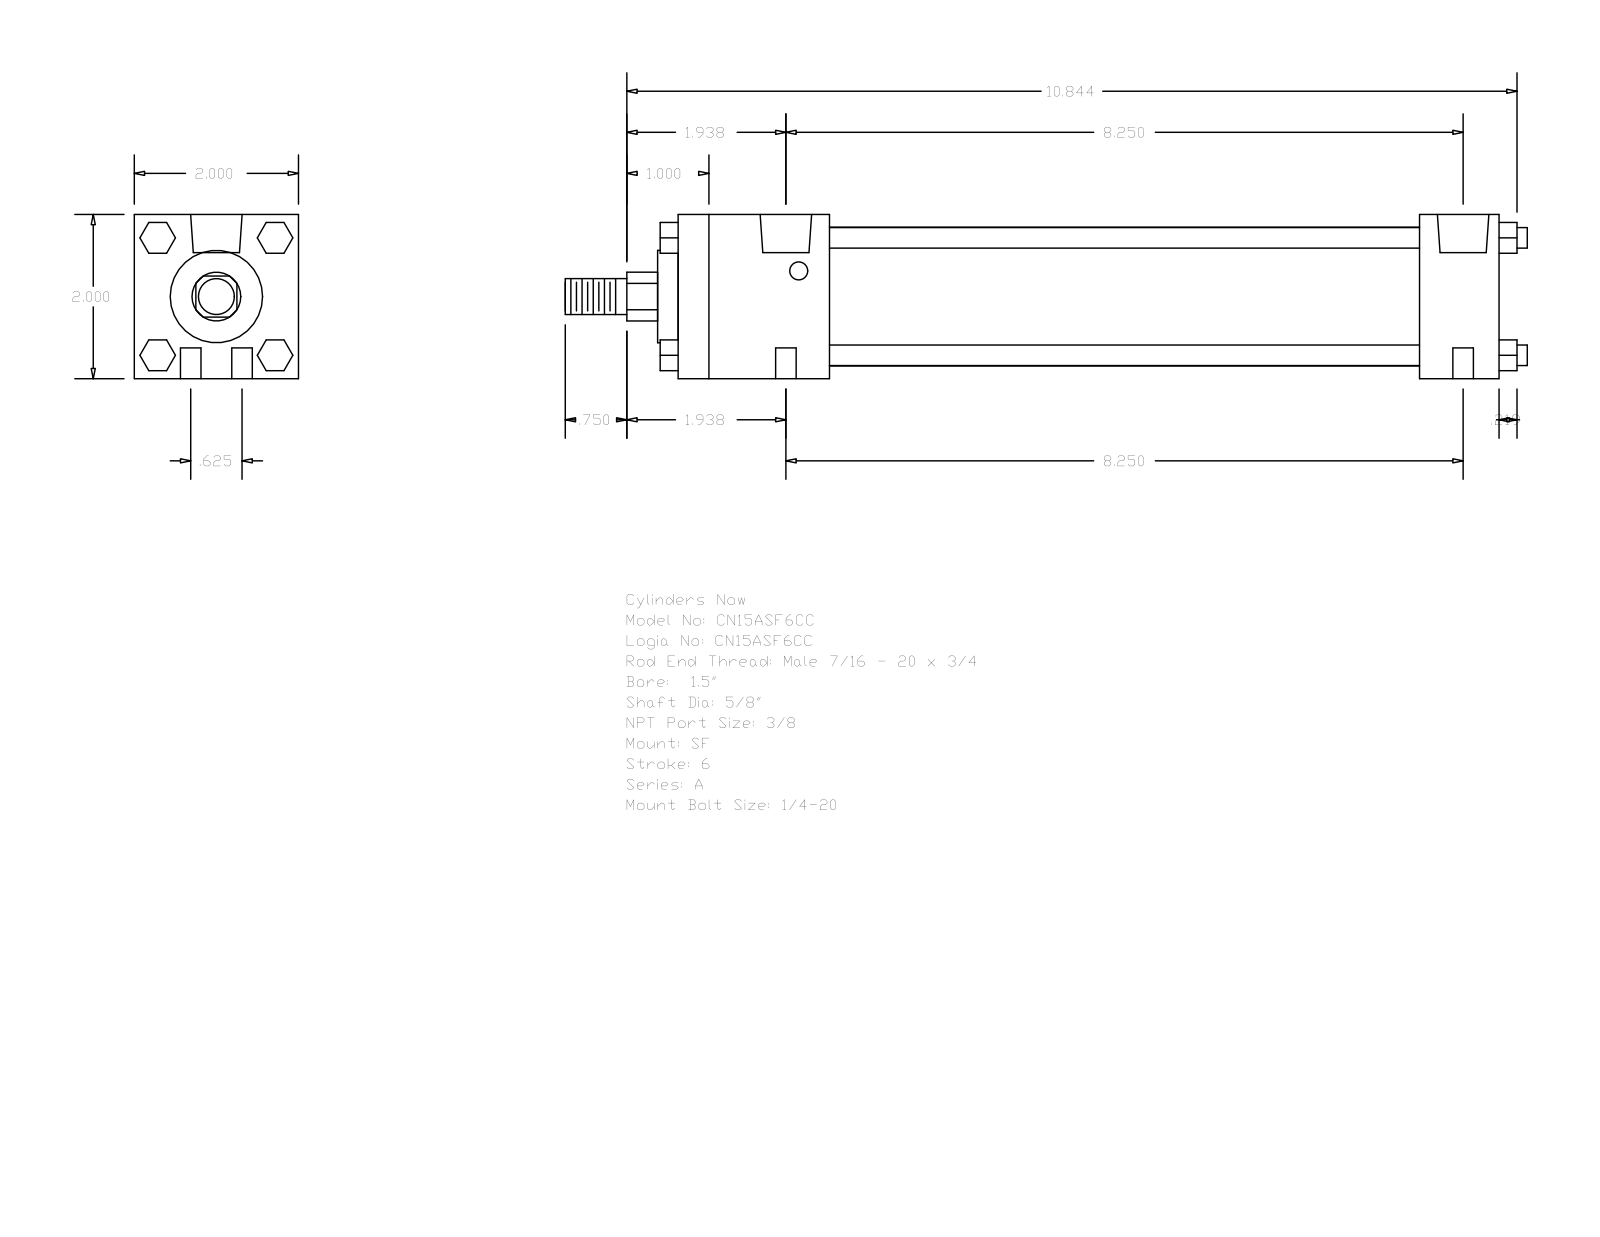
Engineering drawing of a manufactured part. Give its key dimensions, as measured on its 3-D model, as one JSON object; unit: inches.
{"part_name": "A_SF__0150_0.625", "step_written_by": "GSSL Pune (CONFIG_CONTROL_DESIGN)", "units": "inches", "bodies": {"solids": 0, "faces": 124, "planar": 94, "cylindrical": 30, "other": 0}, "overall_size": [11.719, 2, 2], "round_holes": [[0.25, 4], [0.219, 2], [0.627, 2]], "round_bosses_or_shafts": [[0.25, 4], [1.69, 1], [1.125, 1], [0.625, 1], [0.437, 1]], "partial_cylinders_radius": [[0.297, 1]], "face_to_face_distances": [2, 10, 1.844, 9.031, 7.187, 8.156, 0.969, 0.25, 0.375, 2.094], "hole_center_spacings": [0.313, 8.256, 8.25, 0.625, 8.274, 7.937]}
